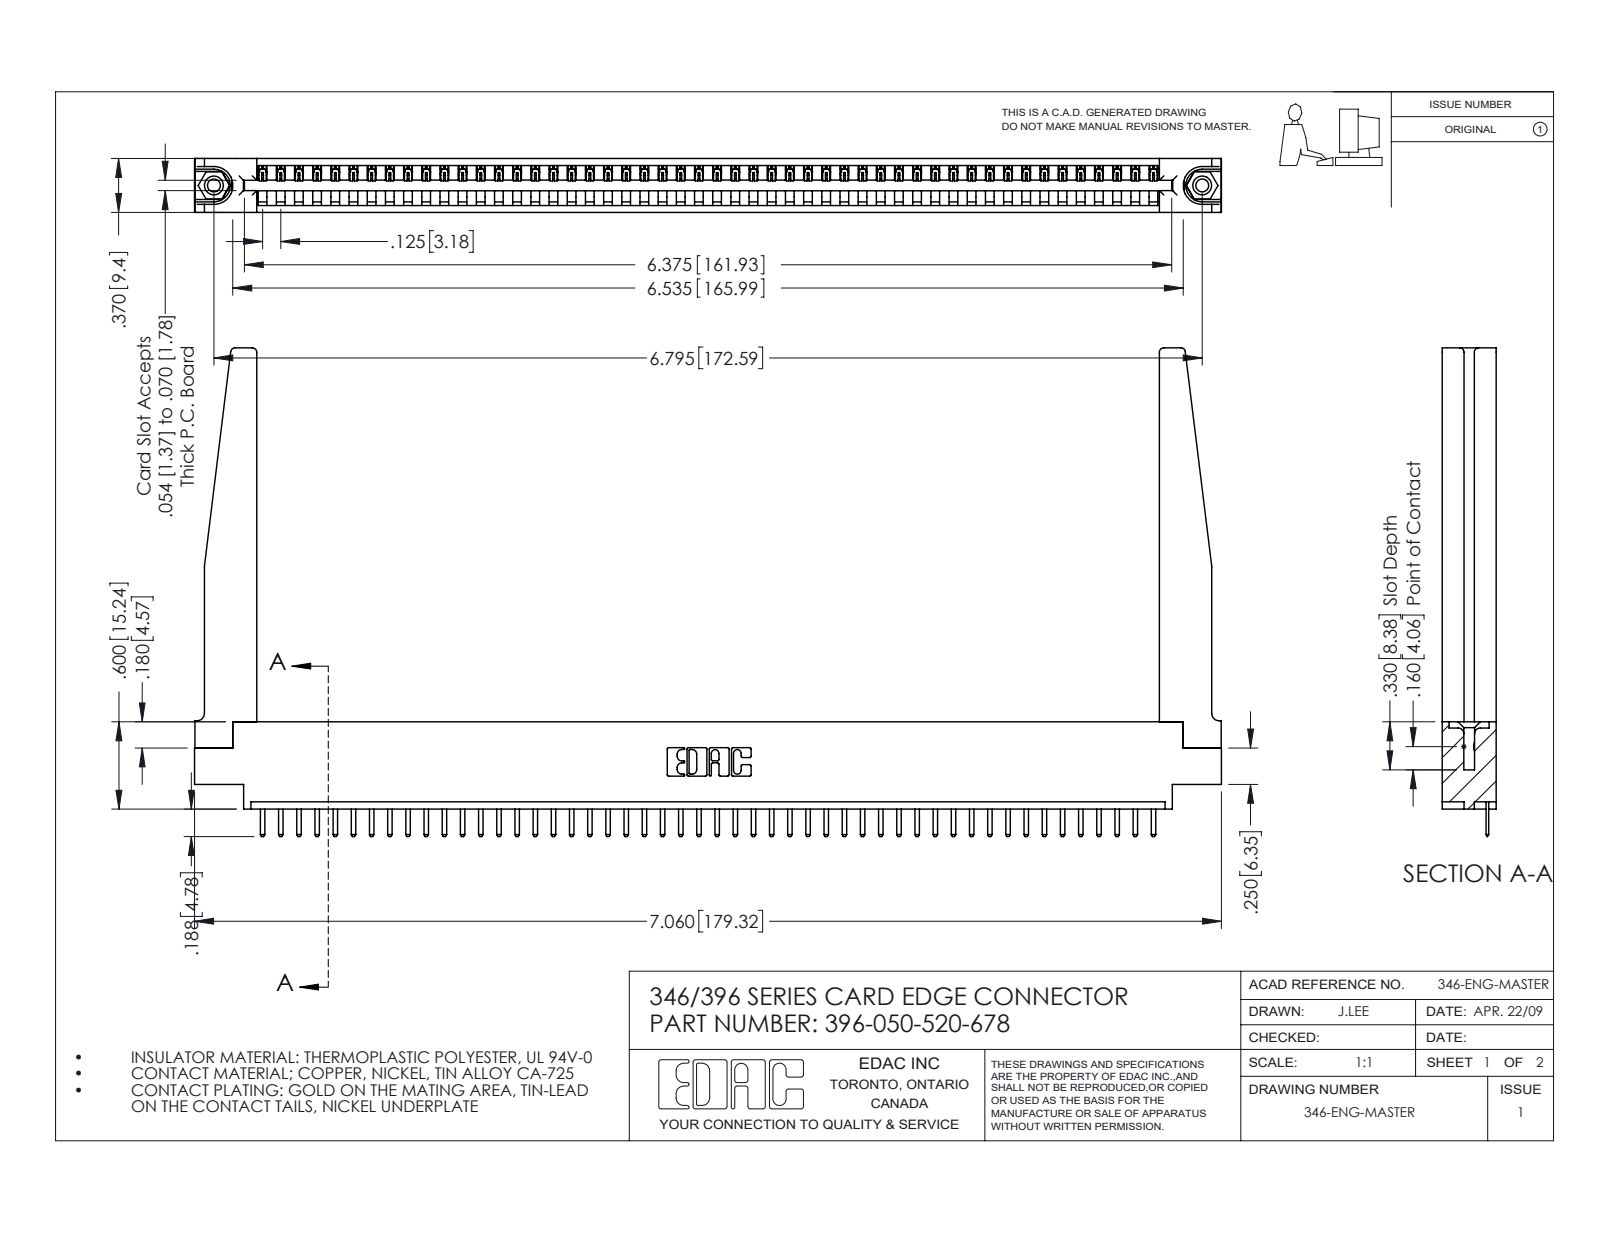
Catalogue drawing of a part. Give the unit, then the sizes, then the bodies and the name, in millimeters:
Units: millimetres
Overall size (bounding box): 179.3 × 85.3 × 9.4
Round holes (diameter × count): ⌀2.3 ×2, ⌀3.2 ×2, ⌀4 ×2, ⌀1.6 ×1
Round bosses / shafts (diameter × count): ⌀3.9 ×2
Partial cylindrical surfaces — rounded edges, fillets, slot ends (radius × count): R0.3 ×102, R0.2 ×100, R0.3 ×22, R0.8 ×8, R0.2 ×6, R0.8 ×6, R0.7 ×3, R0.8 ×2
Main face-to-face distances: 9.4, 1.2, 8.2, 3.8, 1.8, 3.8, 6.4, 5.6, 2.5, 4.4
Hole centre spacings: 6.2, 167.3, 172.6
Volume: 23 830 mm³ · Surface area: 27 460 mm²
Bodies: 55 solids, 3460 faces (2322 planar, 1086 cylindrical, 52 other)
Part name (STEP PRODUCT): 345-292-001_345-293-120; 346 Part_0.170 Offset - 0.156 Dia-TH; 346-220-078_345-220-078; 396-050-520-678 (+1 more)
STEP written by: SolidWorks 2016 (CONFIG_CONTROL_DESIGN)
